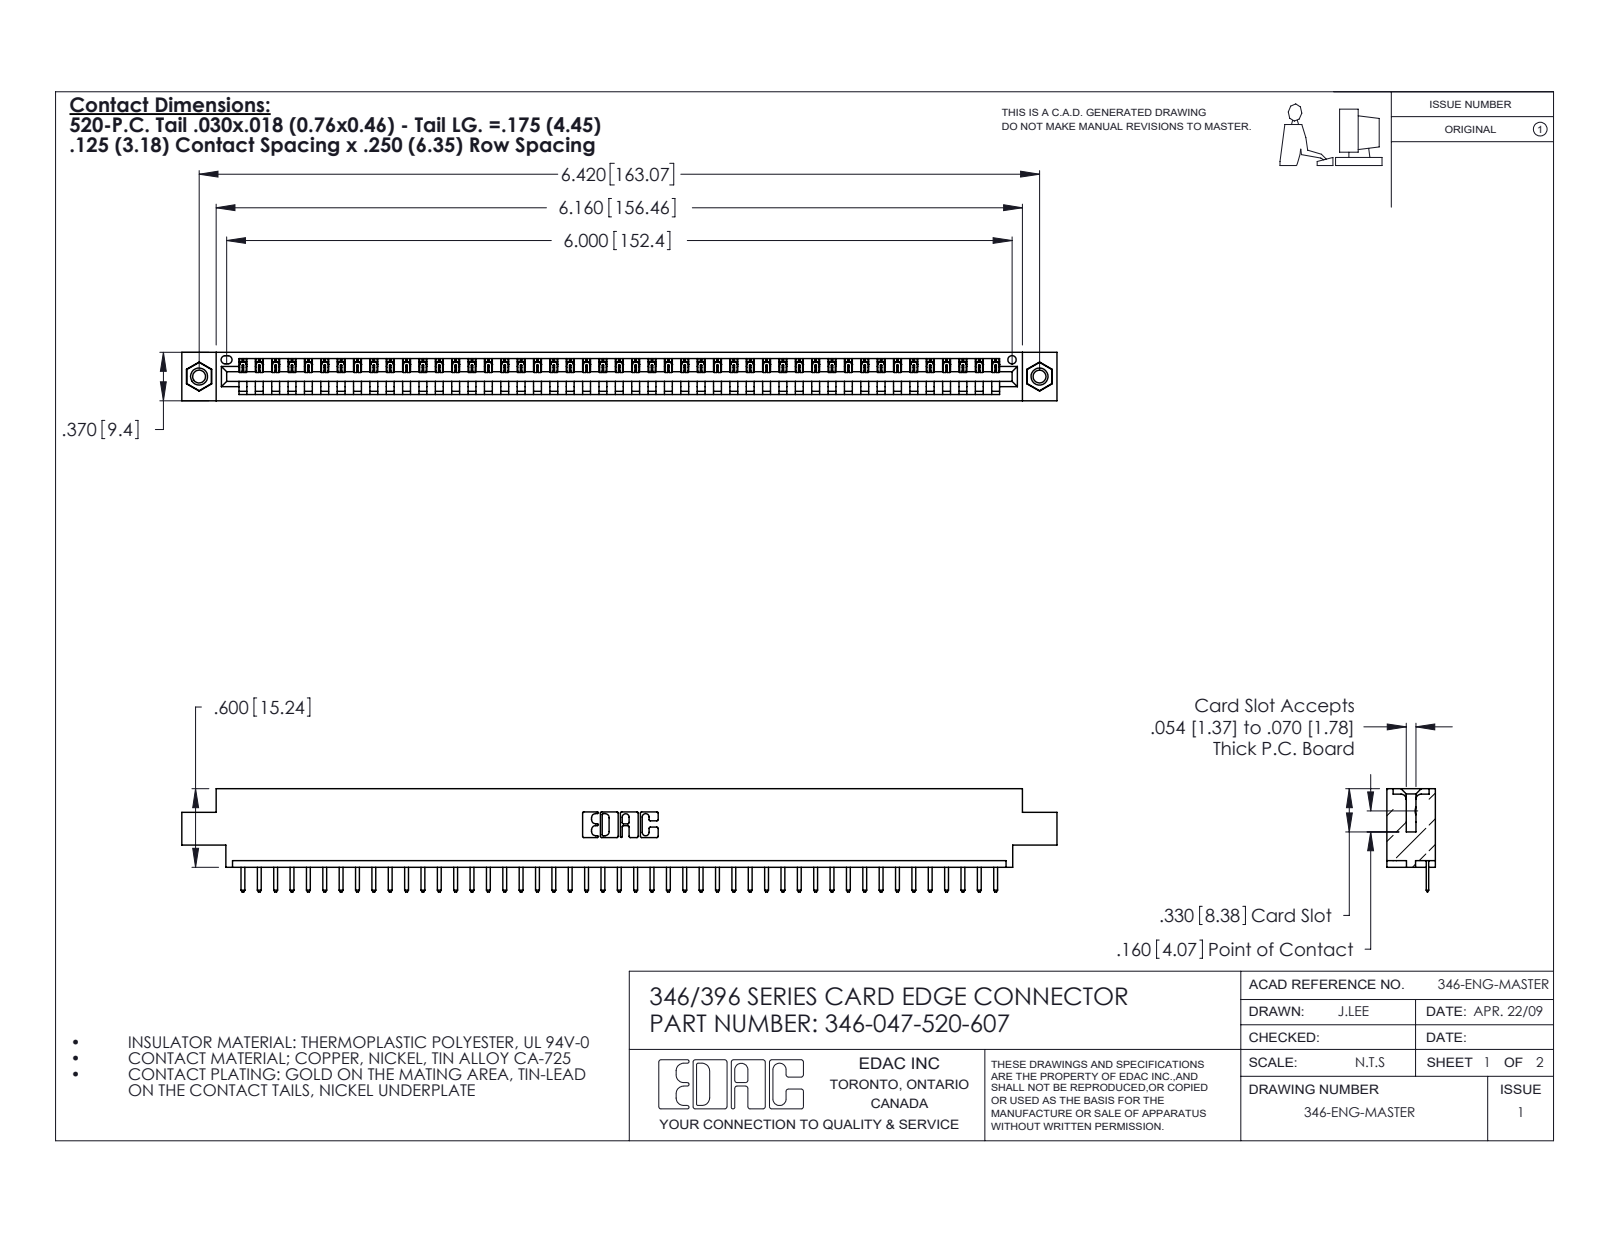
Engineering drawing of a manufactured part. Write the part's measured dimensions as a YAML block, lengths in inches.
part_name: "346-047-520-607; 345-292-001_345-293-120; 345-250-001_345-250-005-103; 346 Part_0.170 Offset - 0.156 Dia-TI"
step_written_by: "SolidWorks 2020 (CONFIG_CONTROL_DESIGN)"
units: inches
bodies: {solids: 50, faces: 3100, planar: 2086, cylindrical: 998, other: 16}
overall_size: [6.685, 0.788, 0.37]
volume: 0.975
surface_area: 30.65
round_holes:
  - {diameter: 0.098, count: 2}
  - {diameter: 0.125, count: 2}
  - {diameter: 0.156, count: 2}
  - {diameter: 0.064, count: 1}
round_bosses_or_shafts:
  - {diameter: 0.155, count: 2}
partial_cylinders:
  - {radius: 0.01, count: 96}
  - {radius: 0.006, count: 94}
  - {radius: 0.01, count: 22}
  - {radius: 0.007, count: 6}
  - {radius: 0.031, count: 6}
  - {radius: 0.026, count: 3}
  - {radius: 0.031, count: 2}
  - {radius: 0.04, count: 2}
face_to_face_distances: [0.048, 0.322, 0.37, 0.25, 0.222, 0.148, 0.1, 0.174, 0.072, 0.298]
hole_center_spacings: [0.246, 6.211, 6.42]
